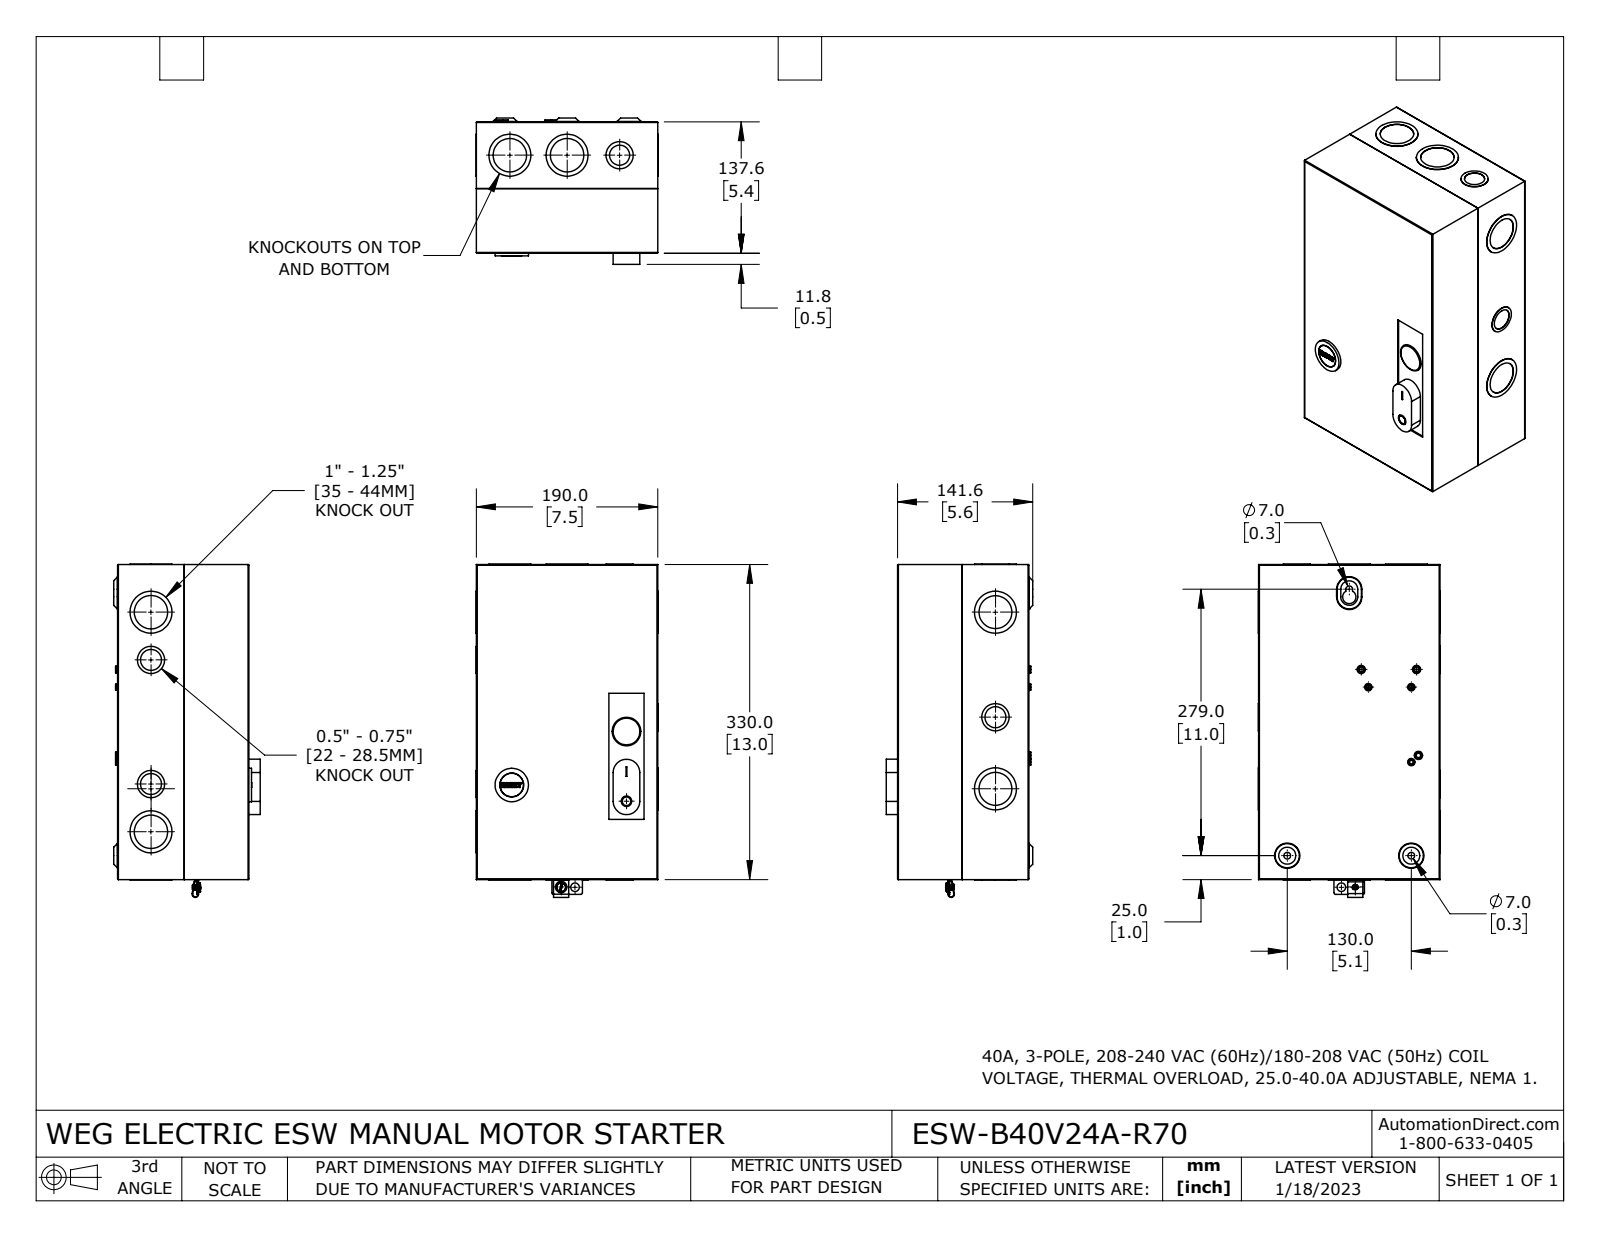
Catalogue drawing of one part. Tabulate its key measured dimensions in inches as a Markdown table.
| quantity | value |
| --- | --- |
| part name | ESW-B40V24A-R70 |
| STEP written by | SolidWorks 2021 (CONFIG_CONTROL_DESIGN) |
| units | inches |
| bodies | 7 solids, 435 faces (161 planar, 221 cylindrical, 53 other) |
| overall size | 13.74 × 7.504 × 6.039 |
| volume | 24.58 in³ |
| surface area | 936.7 in² |
| round holes (diameter × count) | 1.378 × 4, 0.146 × 3, 0.183 × 3, 0.276 × 2, 0.866 × 2, 0.886 × 2, 1.357 × 2, 0.256 × 1, 0.279 × 1, 0.354 × 1, 0.433 × 1, 0.469 × 1 |
| round bosses / shafts (diameter × count) | 1.732 × 4, 1.122 × 3, 0.278 × 3, 0.24 × 3, 1.734 × 2, 1.378 × 1, 1.193 × 1, 1.148 × 1 |
| partial cylindrical surfaces (radius × count) | 0.004 × 34, 0.031 × 8, 0.079 × 3, 0.138 × 3, 0.059 × 2, 0.075 × 2, 0.108 × 2, 0.122 × 2 |
| main face-to-face distances | 0.047, 5.37, 7.433, 5.323, 5.417, 12.945, 7.386, 7.48, 0.071, 12.898 |
| hole center spacings | 0.571, 1.772, 1.969, 2.283, 2.362, 5.118, 7.087, 10.972 |
